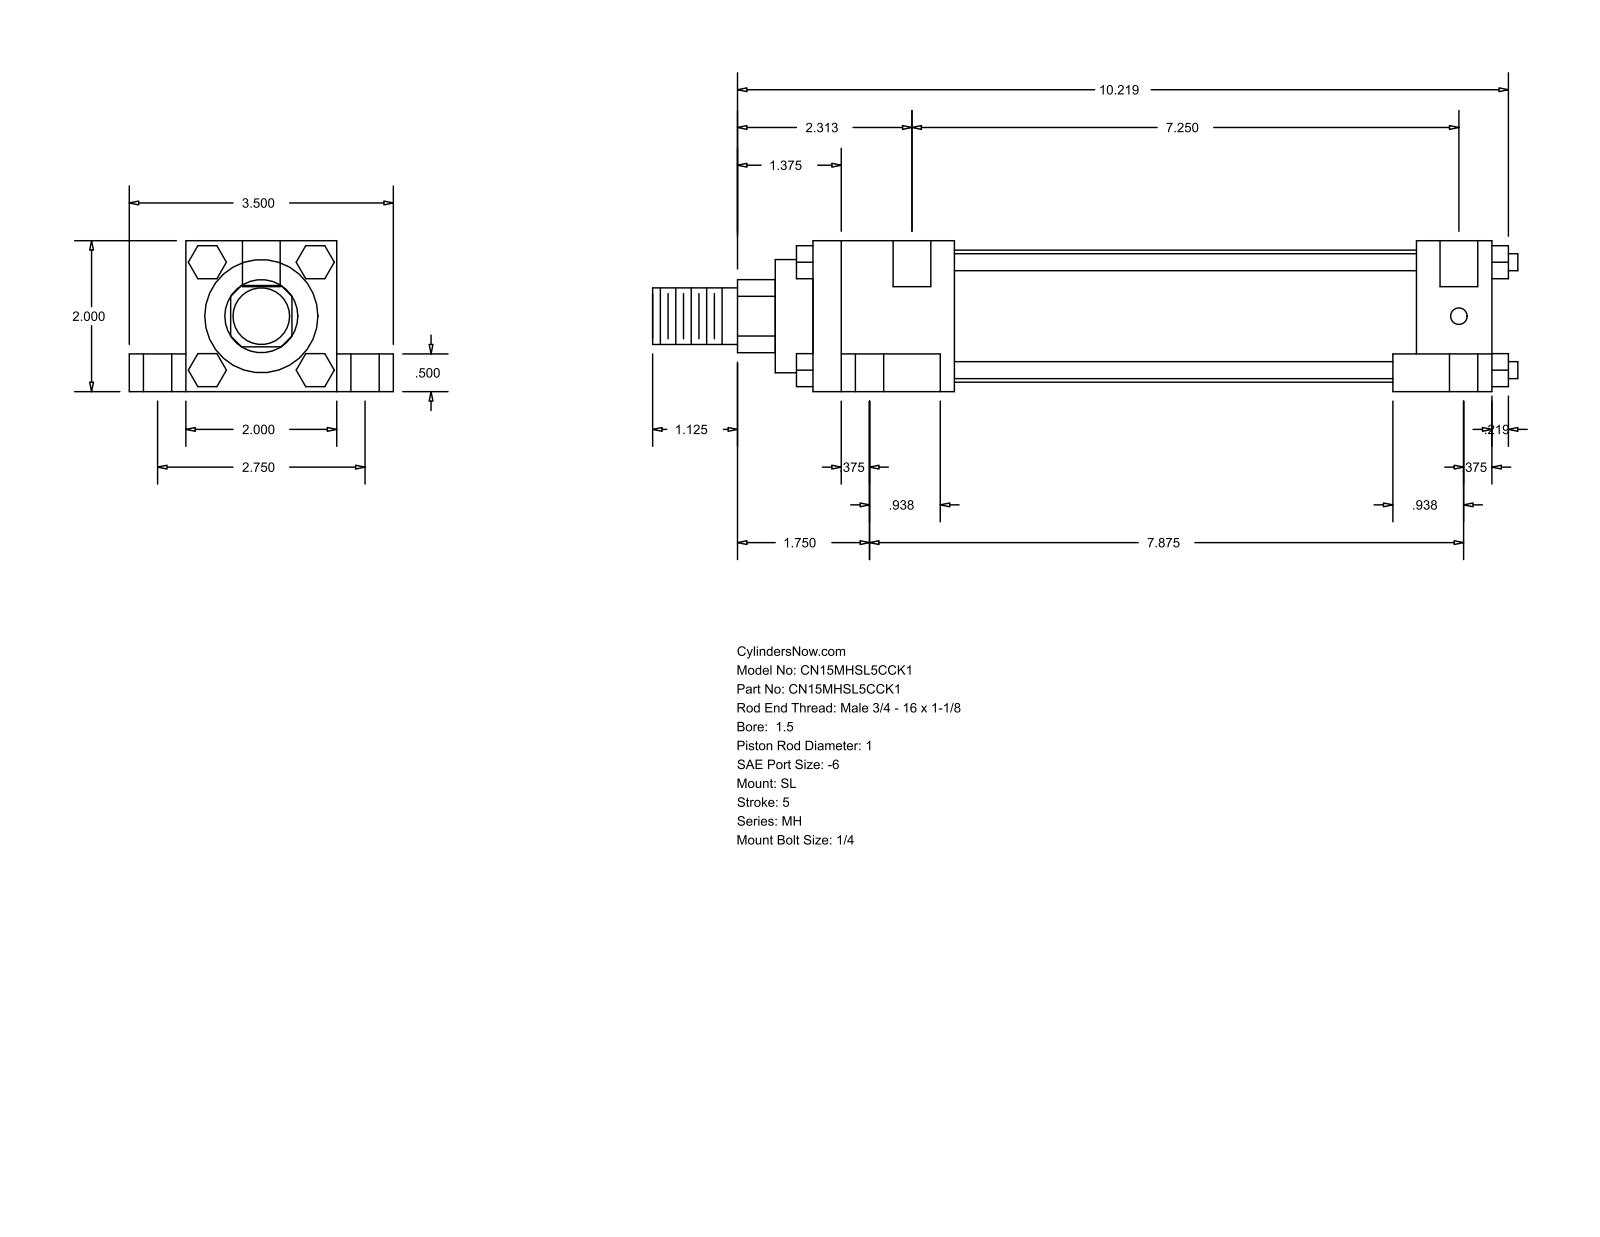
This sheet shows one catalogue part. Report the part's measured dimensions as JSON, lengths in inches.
{"part_name": "MH_SL__0150_1", "step_written_by": "GSSL Pune (CONFIG_CONTROL_DESIGN)", "units": "inches", "bodies": {"solids": 0, "faces": 148, "planar": 112, "cylindrical": 36, "other": 0}, "overall_size": [11.469, 3.5, 2], "round_holes": [[0.219, 4], [0.375, 4], [0.625, 4], [0.5, 2]], "round_bosses_or_shafts": [[0.225, 4], [1.75, 1], [1.5, 1], [1, 1], [0.75, 1]], "partial_cylinders_radius": [[0.484, 1]], "face_to_face_distances": [2, 0.5, 1.5, 0.75, 2.75, 9, 1, 0.375, 1.313, 7.313], "hole_center_spacings": [1.376, 1.443, 1.485, 2.75, 7.375, 7.44, 7.563, 7.875]}
